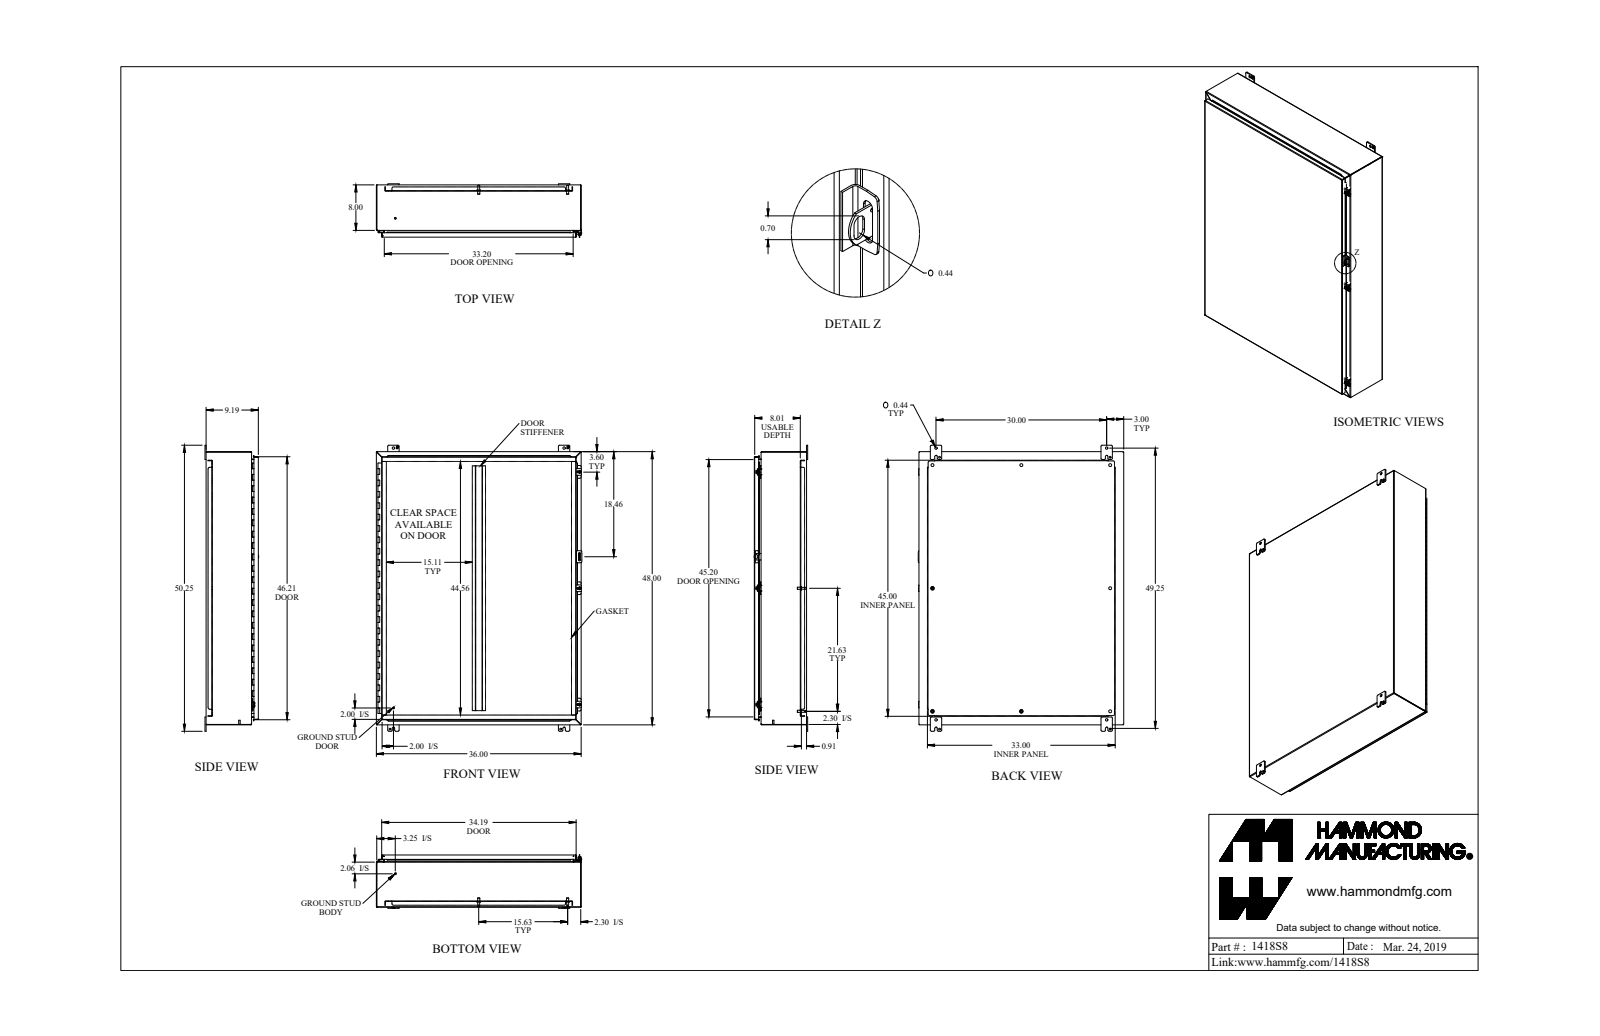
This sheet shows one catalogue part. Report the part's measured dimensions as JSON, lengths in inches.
{"part_name": "1418S8_Default", "step_written_by": "SolidWorks 2019 (CONFIG_CONTROL_DESIGN)", "units": "inches", "bodies": {"solids": 54, "faces": 1751, "planar": 1003, "cylindrical": 638, "other": 110}, "overall_size": [50.25, 36.125, 9.437], "volume_in3": 590.3, "surface_area_in2": 15247, "round_holes": [[0.5, 8], [0.307, 4], [0.313, 4], [0.437, 4], [0.445, 4], [0.213, 3], [0.265, 3], [0.375, 3], [0.125, 1], [0.187, 1]], "round_bosses_or_shafts": [[0.65, 8], [0.375, 8], [0.33, 8], [1, 4], [0.5, 3], [0.39, 3], [0.244, 3], [0.281, 2]], "partial_cylinders_radius": [[0.188, 38], [0.036, 24], [0.108, 24], [0.25, 24], [0.048, 19], [0.143, 19], [0.116, 16], [0.04, 8]], "face_to_face_distances": [0.072, 9.113, 9.041, 9.185, 0.095, 0.937, 1.009, 8.081, 8.009, 1.032], "hole_center_spacings": [43.25, 45.986, 38.003, 15.625, 30, 1.735, 2.434, 3.064]}
